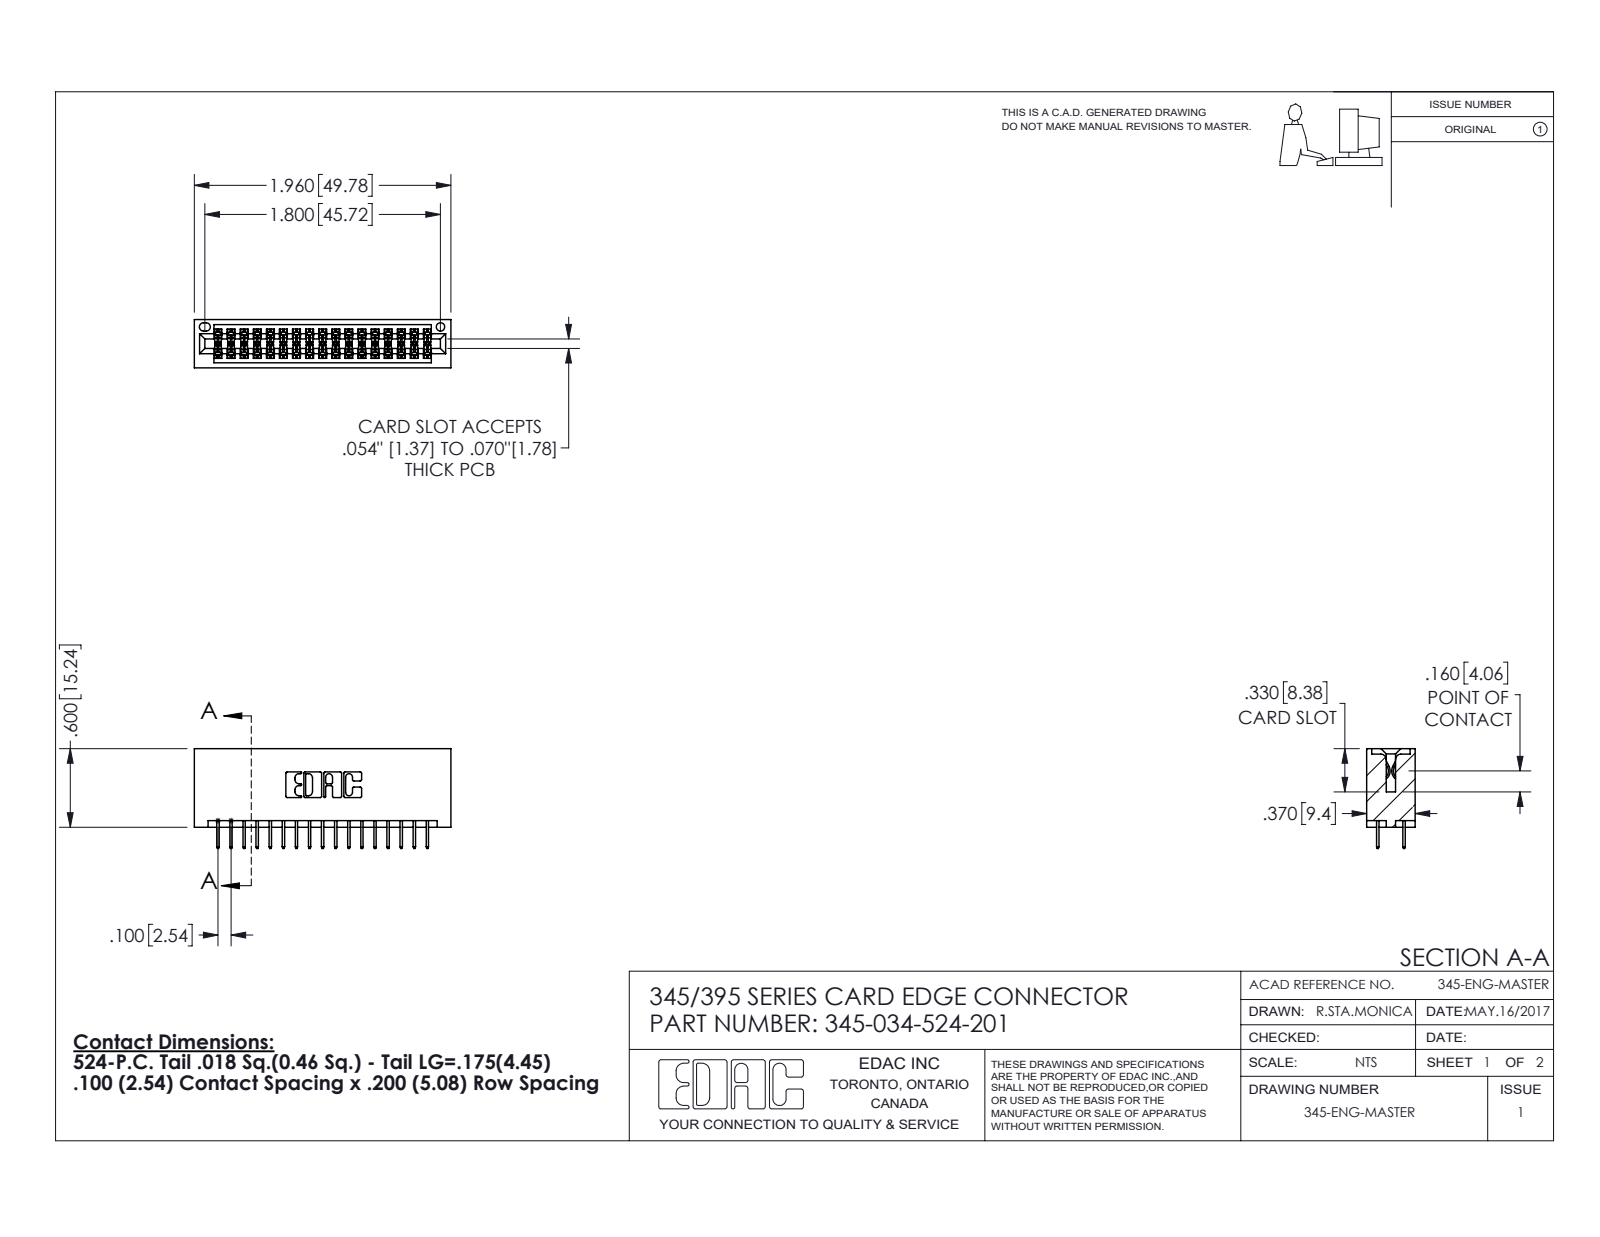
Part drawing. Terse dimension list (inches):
name: 345-292-001_345-293-124; 345 Part_No Mounting Lugs; 345-034-524-201
written by: SolidWorks 2016 (CONFIG_CONTROL_DESIGN)
unit: in
bodies: 35 solids, 1954 faces (1402 planar, 552 cylindrical, 0 other)
size: 1.96 × 0.762 × 0.37
volume: 0.315 in³; area: 11.35 in²
holes: 1× ⌀0.064
rounds: 51× R0.006, 22× R0.01, 6× R0.007, 6× R0.031, 3× R0.026, 2× R0.014, 2× R0.019, 2× R0.022
face distances: 0.298, 0.072, 0.2, 0.37, 0.098, 0.272, 0.025, 0.225, 0.1, 0.072
